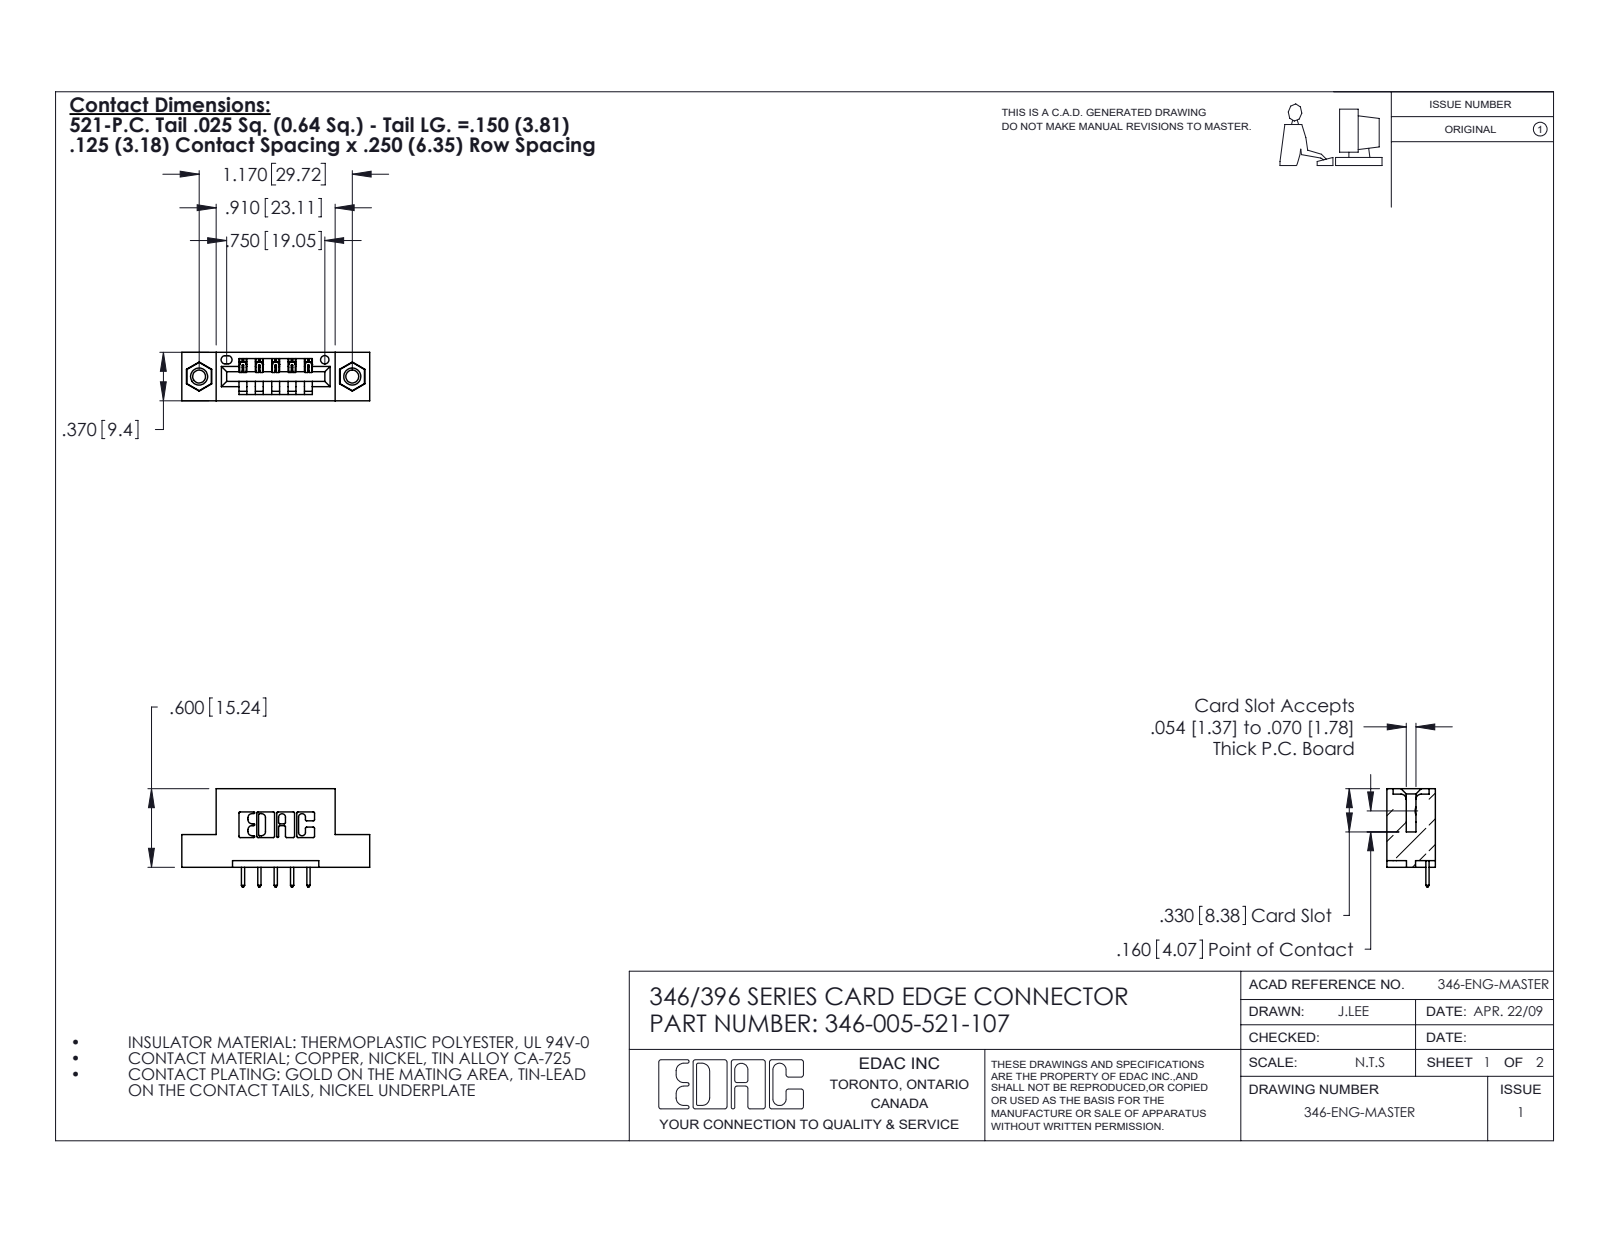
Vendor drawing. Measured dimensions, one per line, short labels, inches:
name: 346-005-521-107; 345-292-001_345-293-121; 346 Part_Flush Mounting Lugs - 0.156 Dia-TI; 345-250-001_345-250-005-103
written by: SolidWorks 2020 (CONFIG_CONTROL_DESIGN)
unit: in
bodies: 8 solids, 472 faces (308 planar, 148 cylindrical, 16 other)
size: 1.435 × 0.75 × 0.37
volume: 0.196 in³; area: 5.559 in²
holes: 2× ⌀0.098, 2× ⌀0.125, 2× ⌀0.156, 1× ⌀0.064
bosses: 2× ⌀0.155
rounds: 22× R0.01, 10× R0.006, 10× R0.01, 6× R0.007, 6× R0.031, 3× R0.026, 2× R0.031, 2× R0.04
face distances: 0.25, 0.37, 0.048, 0.322, 0.55, 0.148, 0.222, 0.1, 0.174, 0.125
hole spacings: 0.246, 0.969, 1.17
